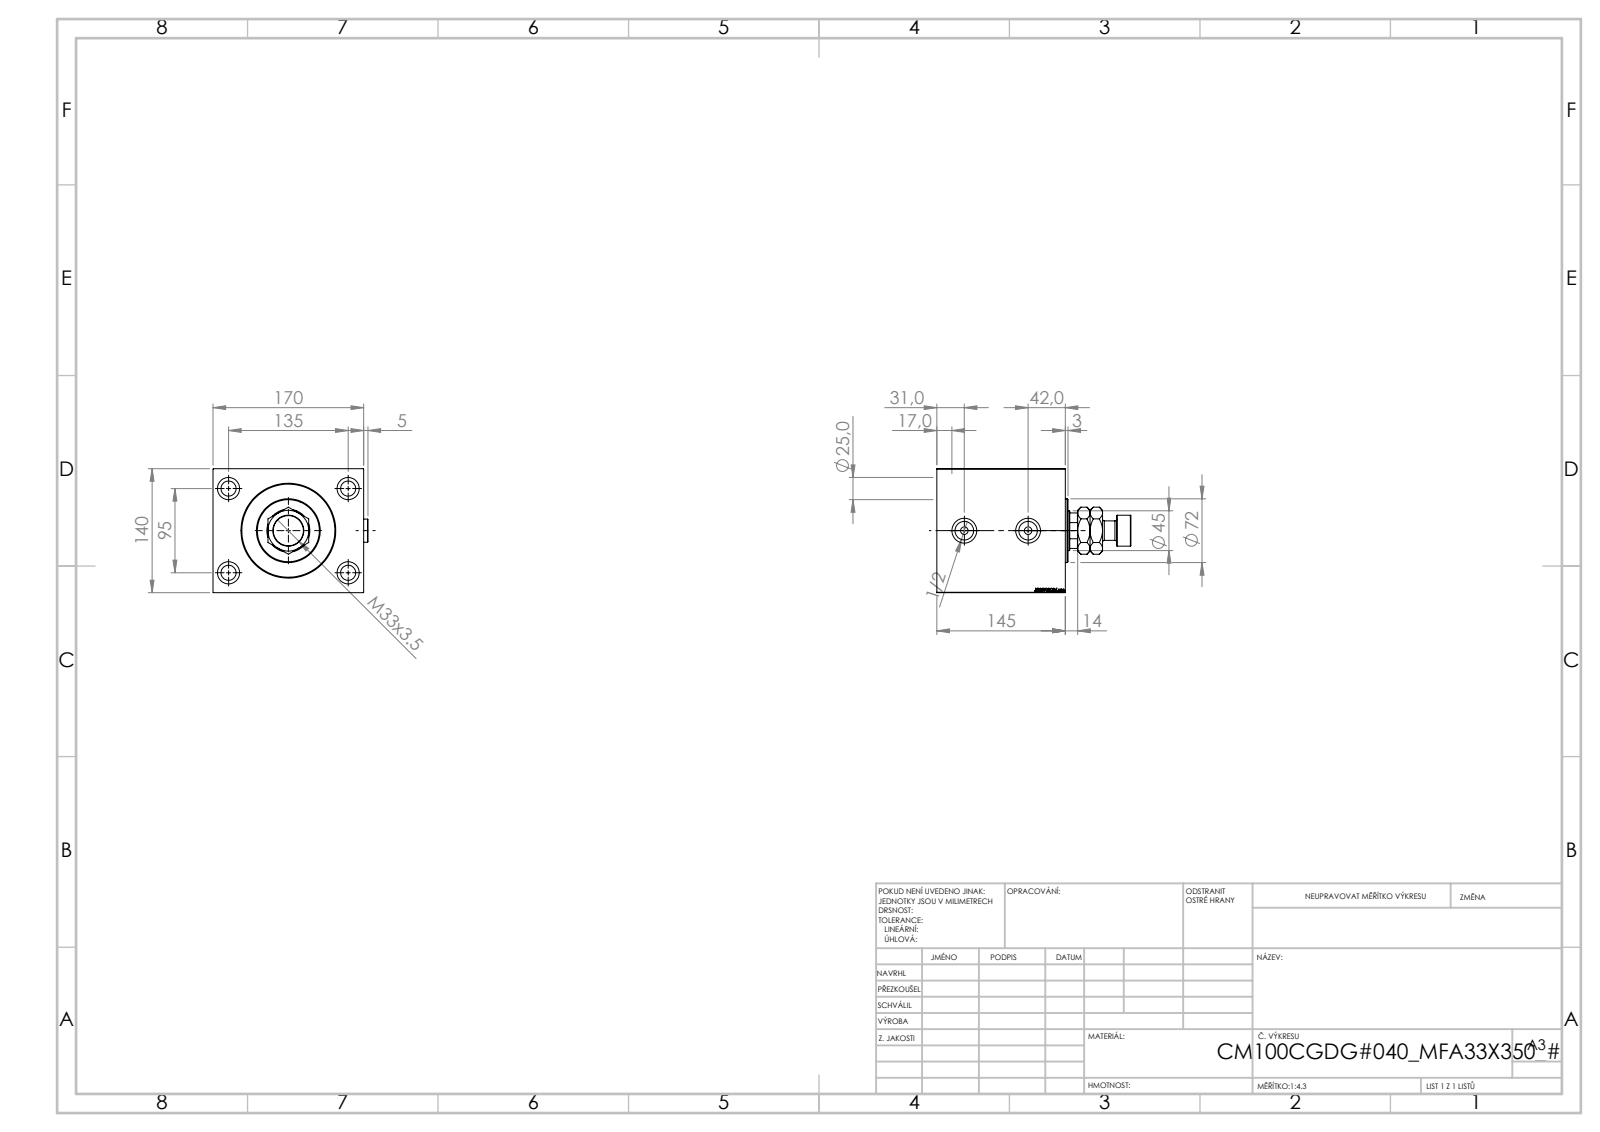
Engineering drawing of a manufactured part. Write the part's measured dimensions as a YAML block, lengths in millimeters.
part_name: "Zatka_OIL_PORT; V450CM_C_VCP; V450CM_VC_B; MFA (+1 more)"
step_written_by: "SolidWorks 2019 (CONFIG_CONTROL_DESIGN)"
units: millimeters
bodies: {solids: 6, faces: 969, planar: 459, cylindrical: 80, other: 430}
overall_size: [219, 174.9, 140]
volume: 3264000
surface_area: 266251
round_holes:
  - {diameter: 17, count: 4}
  - {diameter: 25, count: 4}
  - {diameter: 8.5, count: 2}
  - {diameter: 20.96, count: 2}
  - {diameter: 28, count: 2}
  - {diameter: 31.5, count: 1}
  - {diameter: 45, count: 1}
  - {diameter: 48.5, count: 1}
  - {diameter: 100, count: 1}
  - {diameter: 102, count: 1}
  - {diameter: 105, count: 1}
round_bosses_or_shafts:
  - {diameter: 26, count: 2}
  - {diameter: 72, count: 1}
  - {diameter: 35, count: 1}
  - {diameter: 22, count: 1}
partial_cylinders:
  - {radius: 22, count: 1}
face_to_face_distances: [140, 170, 145, 51, 94, 21.6, 29.4, 123.4, 10, 31.6]
hole_center_spacings: [82.54, 95, 135, 165.08, 72]
